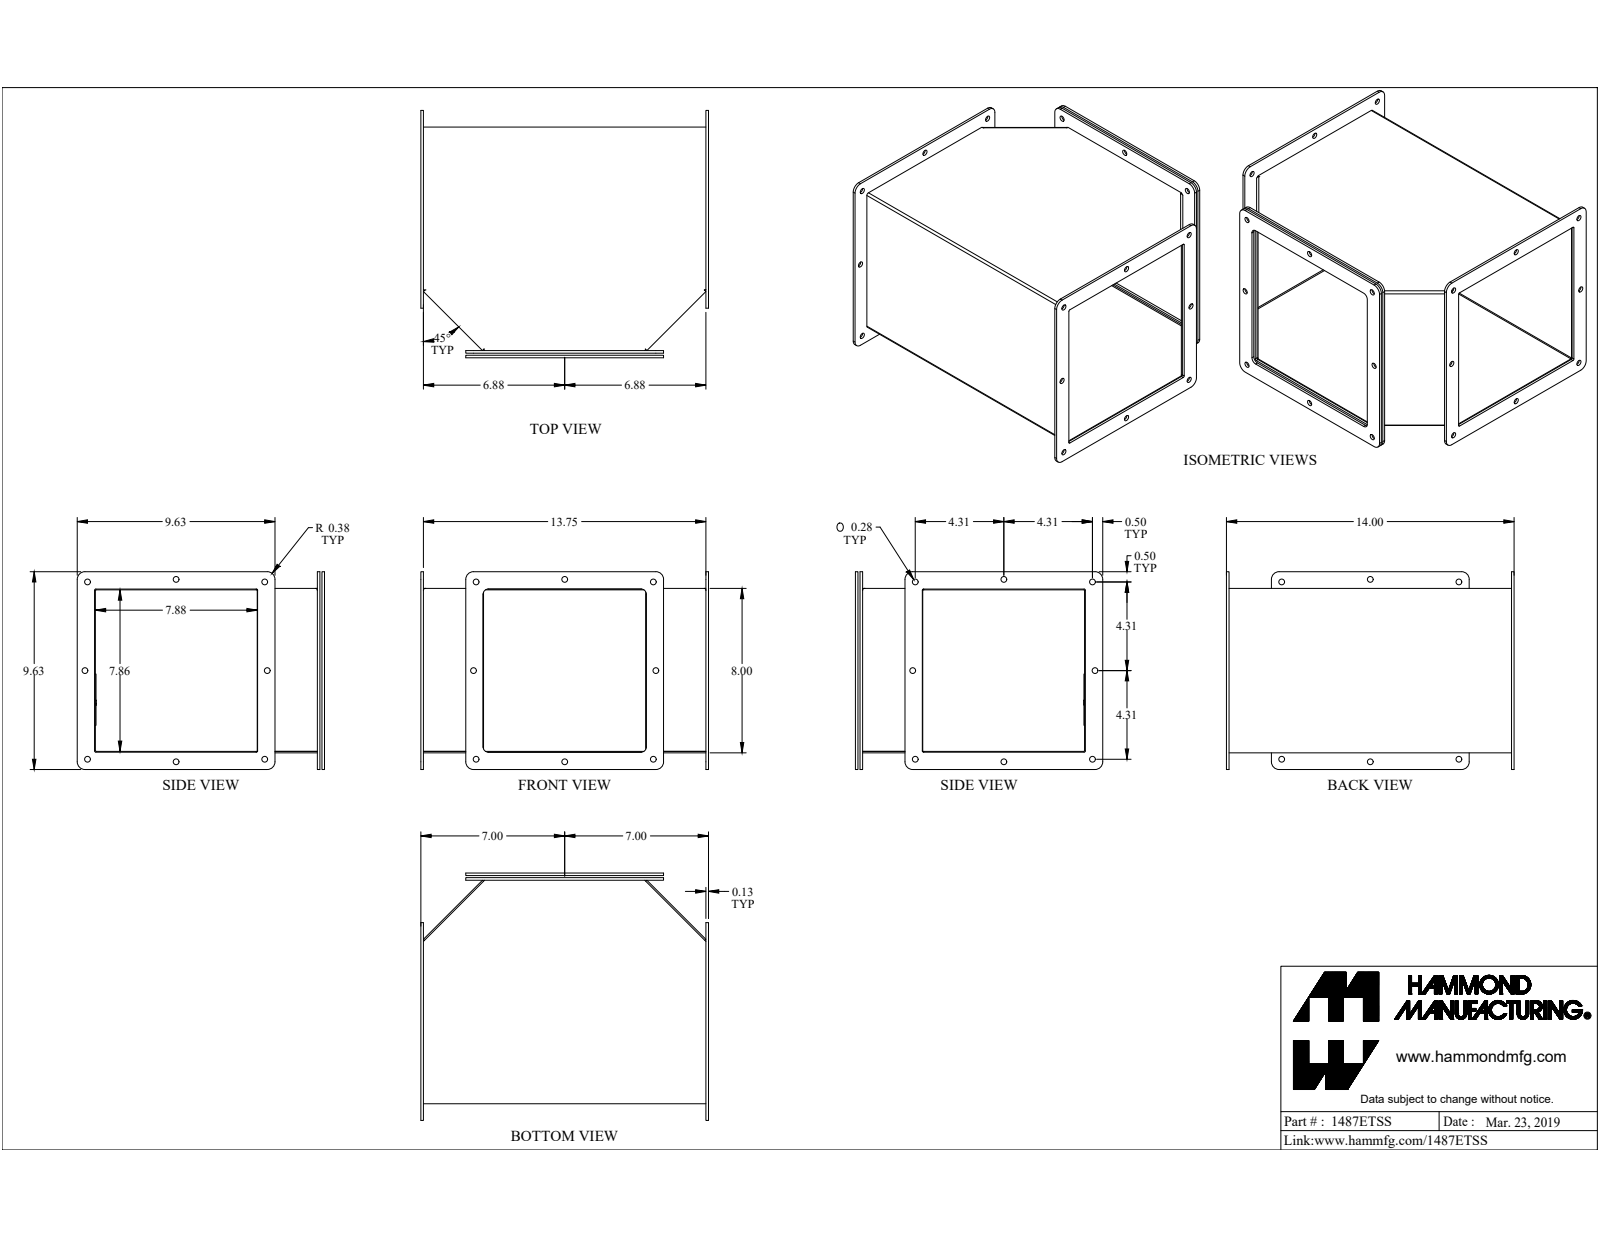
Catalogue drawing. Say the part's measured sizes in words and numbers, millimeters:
The part is named "1487ETSS". Its 3-D file was written by "SolidWorks 2019 (CONFIG_CONTROL_DESIGN)". It is 9 solids with 312 faces: 187 planar, 98 cylindrical and 27 other. Overall it measures 355.6 by 314.5 by 244.5 millimeters. Its volume is 778 400 cubic millimeters and its surface area 778 100 square millimeters. Round holes: 16 of diameter 7.1, 1 of diameter 5, 1 of diameter 6.6, 1 of diameter 8.9. Round bosses or shafts: 1 of diameter 12.7, 1 of diameter 6.4. Partial cylindrical surfaces (rounded edges, fillets, slot ends): 12 of radius 9.5, 8 of radius 1.6, 6 of radius 0.5, 4 of radius 0.9, 4 of radius 2.7, 4 of radius 6.4. The main face-to-face distances are 1.8, 201.4, 203.2, 199.5, 3.2, 352.4, 349.3, 276.2, 274.4, 8.9. The hole center spacings are 109.6, 247.8, 159.4, 219.1, 225.4, 109.6, 219.1, 247.8.
